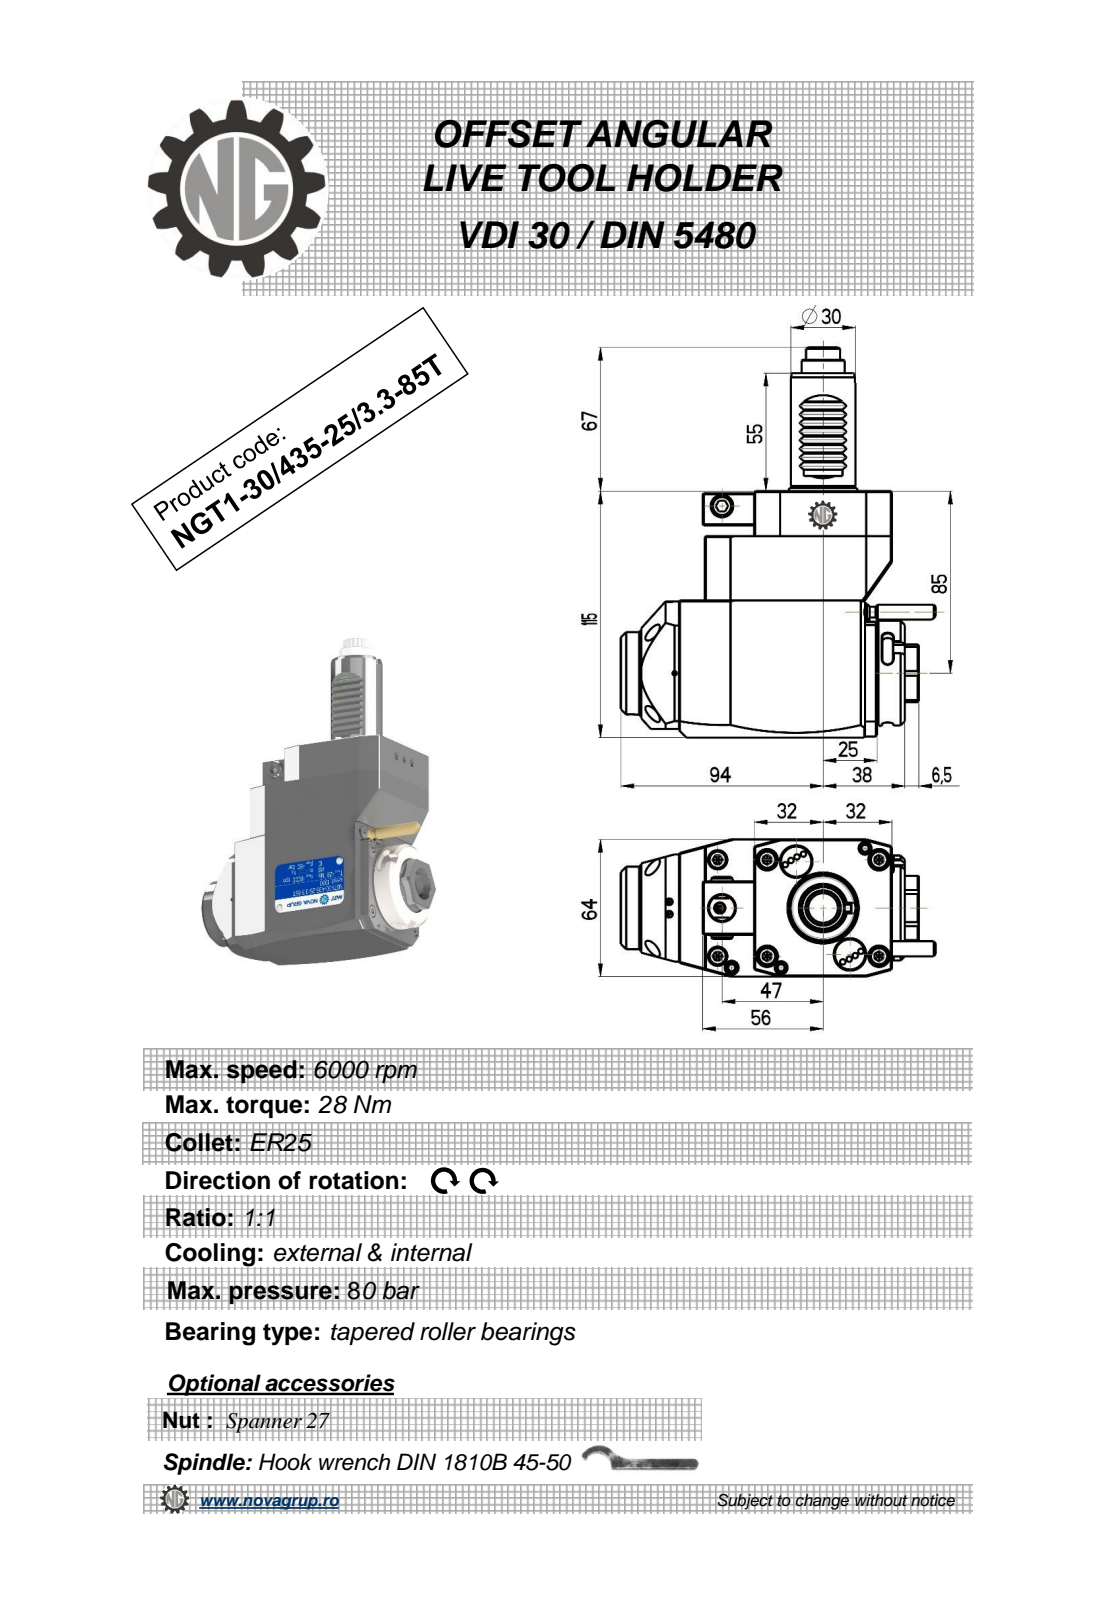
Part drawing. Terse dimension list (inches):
name: NGT1_30_435_25_3_3_85T
written by: PRO/ENGINEER BY PARAMETRIC TECHNOLOGY CORPORATION, 2010280 (CONFIG_CONTROL_DESIGN)
unit: in
bodies: 1 solid, 464 faces (221 planar, 151 cylindrical, 92 other)
size: 7.165 × 5.763 × 2.52
volume: 44.27 in³; area: 95.51 in²
holes: 1× ⌀0.098, 1× ⌀0.118, 1× ⌀0.374, 1× ⌀0.472, 1× ⌀0.709
bosses: 2× ⌀0.315, 1× ⌀1.929, 1× ⌀1.654, 1× ⌀1.516, 1× ⌀1.181, 1× ⌀0.787, 1× ⌀0.394, 1× ⌀0.276
rounds: 36× R0.078, 16× R0.012, 6× R0.098, 2× R7.087, 1× R0.167, 1× R0.177, 1× R0.279, 1× R0.312
face distances: 2.52, 4.528, 0.276, 3.701, 3.15, 3.425, 0.236, 0.512, 0.827, 0.492
hole spacings: 1.348, 2.032, 3.012
